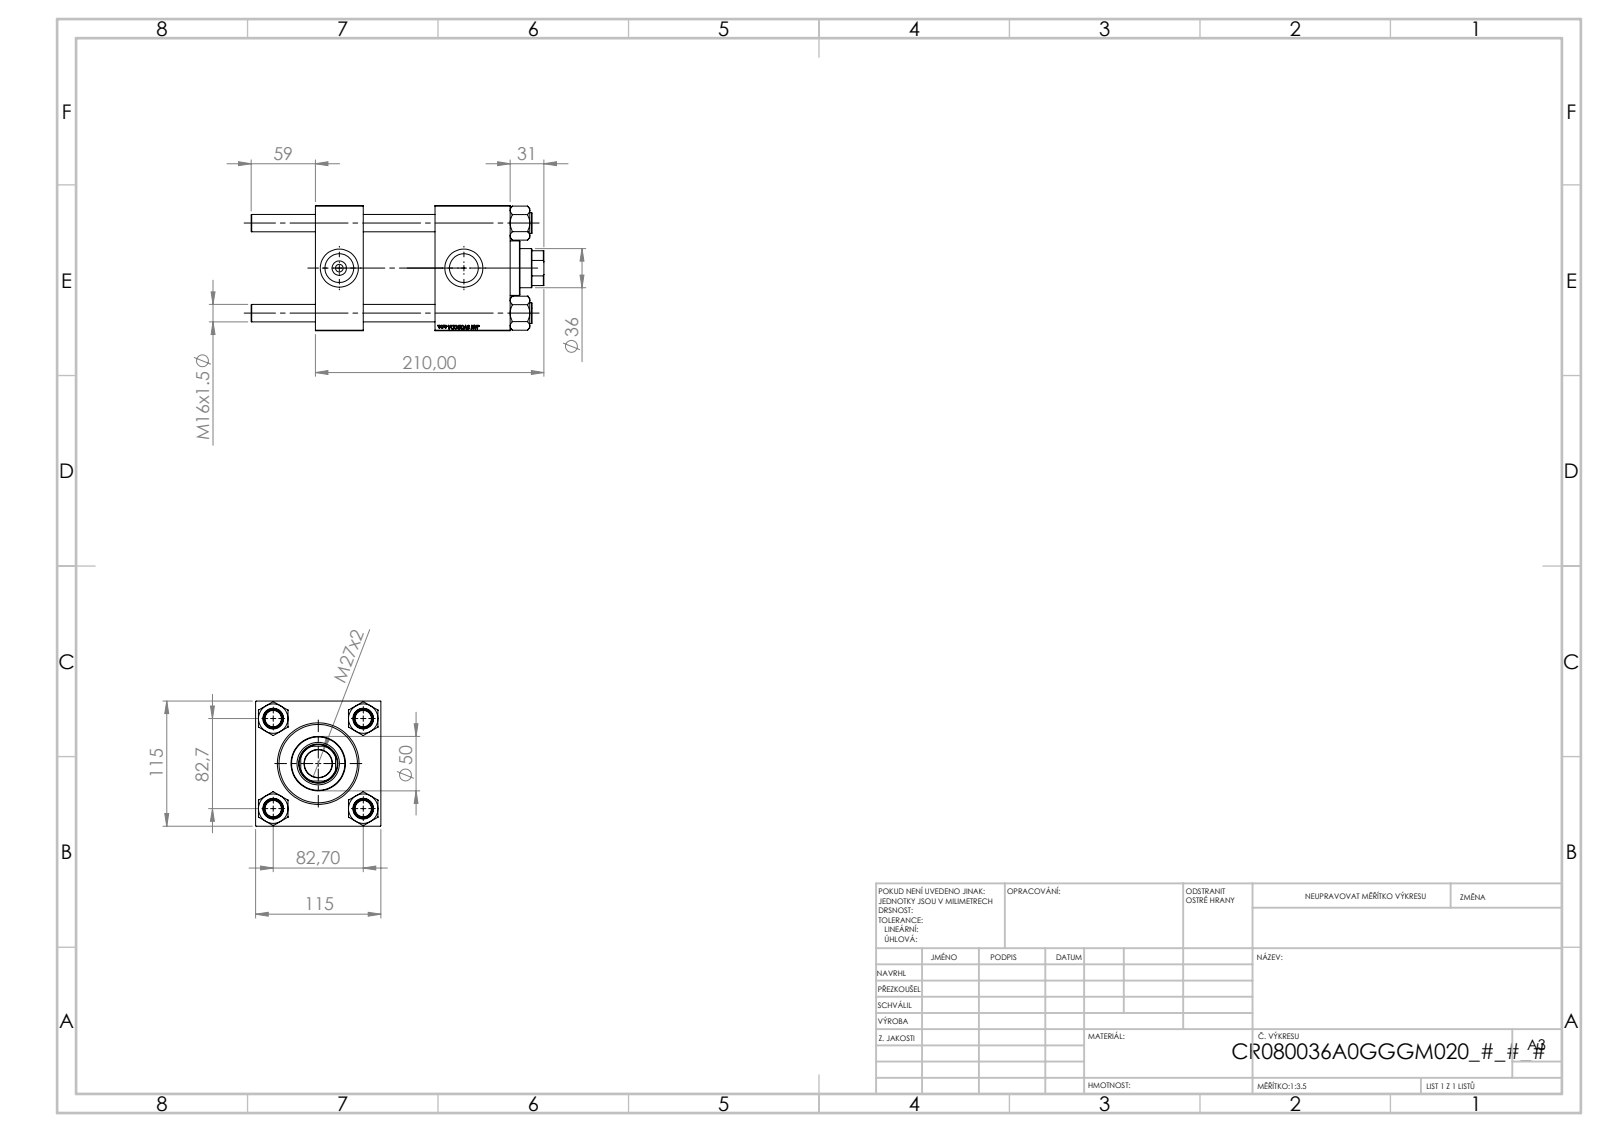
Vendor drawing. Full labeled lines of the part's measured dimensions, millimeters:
Part name (STEP PRODUCT): CR025_012_A_0_G_A_G_M_020_+#_##_TYCINKA; V215CR_VCP; V215_VC_A; NUT_M5 (+1 more)
STEP written by: SolidWorks 2019 (CONFIG_CONTROL_DESIGN)
Units: millimetres
Bodies: 11 solids, 1182 faces (567 planar, 79 cylindrical, 536 other)
Overall size (bounding box): 269 × 115 × 115
Volume: 1 863 000 mm³ · Surface area: 295 407 mm²
Round holes (diameter × count): ⌀16 ×4, ⌀7 ×2, ⌀26.44 ×2, ⌀35 ×2, ⌀25.5 ×1, ⌀36 ×1, ⌀39 ×1, ⌀61 ×1, ⌀72 ×1, ⌀80 ×1
Round bosses / shafts (diameter × count): ⌀19 ×4, ⌀86 ×1, ⌀50 ×1
Partial cylindrical surfaces — rounded edges, fillets, slot ends (radius × count): R17.5 ×1
Main face-to-face distances: 115, 44, 179, 135, 110, 69, 66, 20, 89, 150.3
Hole centre spacings: 58.48, 82.7, 116.96, 114.44
